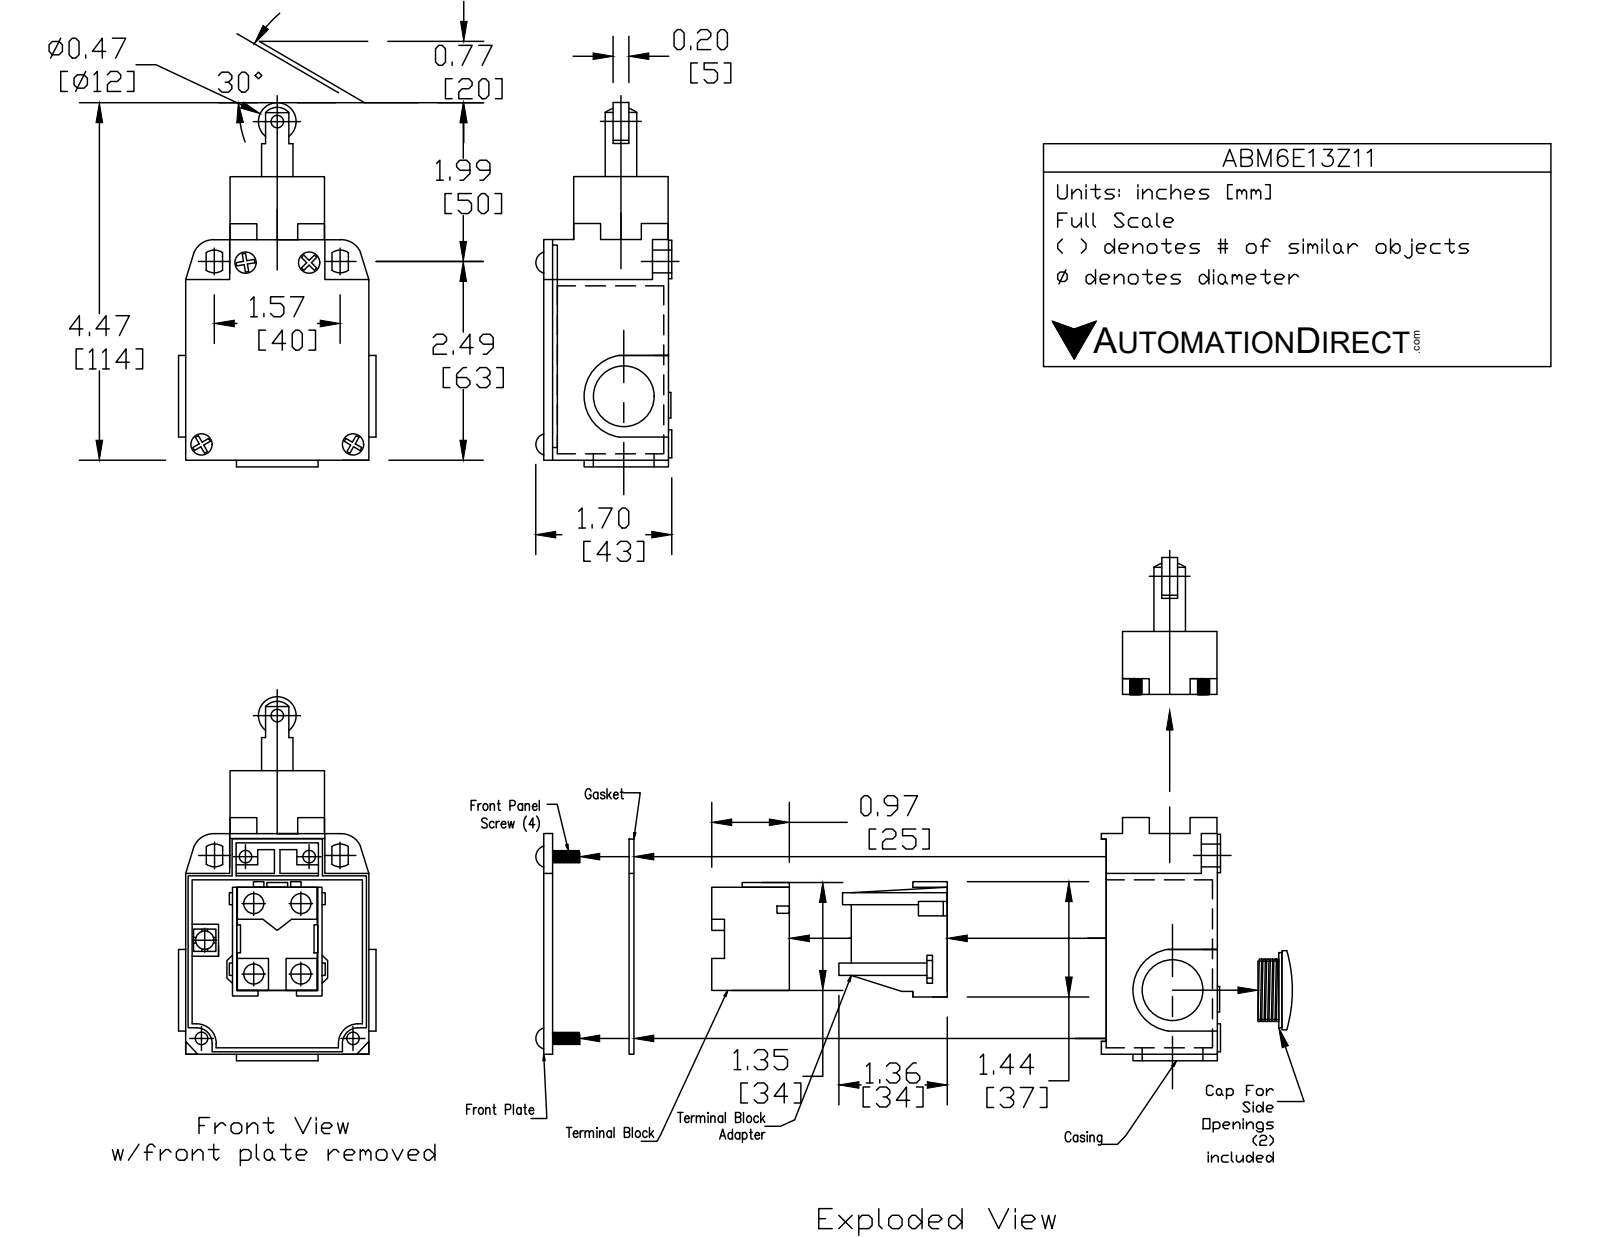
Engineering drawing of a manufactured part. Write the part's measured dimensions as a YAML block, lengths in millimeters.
part_name: "ABM6E13Z11"
step_written_by: "SolidWorks 2017 (AUTOMOTIVE_DESIGN)"
units: millimeters
bodies: {solids: 4, faces: 188, planar: 86, cylindrical: 72, other: 30}
overall_size: [115.4, 62, 43.3]
volume: 166800
surface_area: 26750
round_holes:
  - {diameter: 17, count: 2}
  - {diameter: 19, count: 2}
  - {diameter: 10, count: 1}
round_bosses_or_shafts:
  - {diameter: 7, count: 4}
  - {diameter: 12, count: 3}
  - {diameter: 9, count: 2}
partial_cylinders:
  - {radius: 1.5, count: 12}
  - {radius: 1, count: 4}
  - {radius: 3.7, count: 2}
  - {radius: 6.5, count: 2}
  - {radius: 13, count: 2}
  - {radius: 11.5, count: 1}
  - {radius: 12, count: 1}
face_to_face_distances: [39.5, 44, 14, 58, 30, 2, 70, 13, 6, 57.5]
hole_center_spacings: [1]
